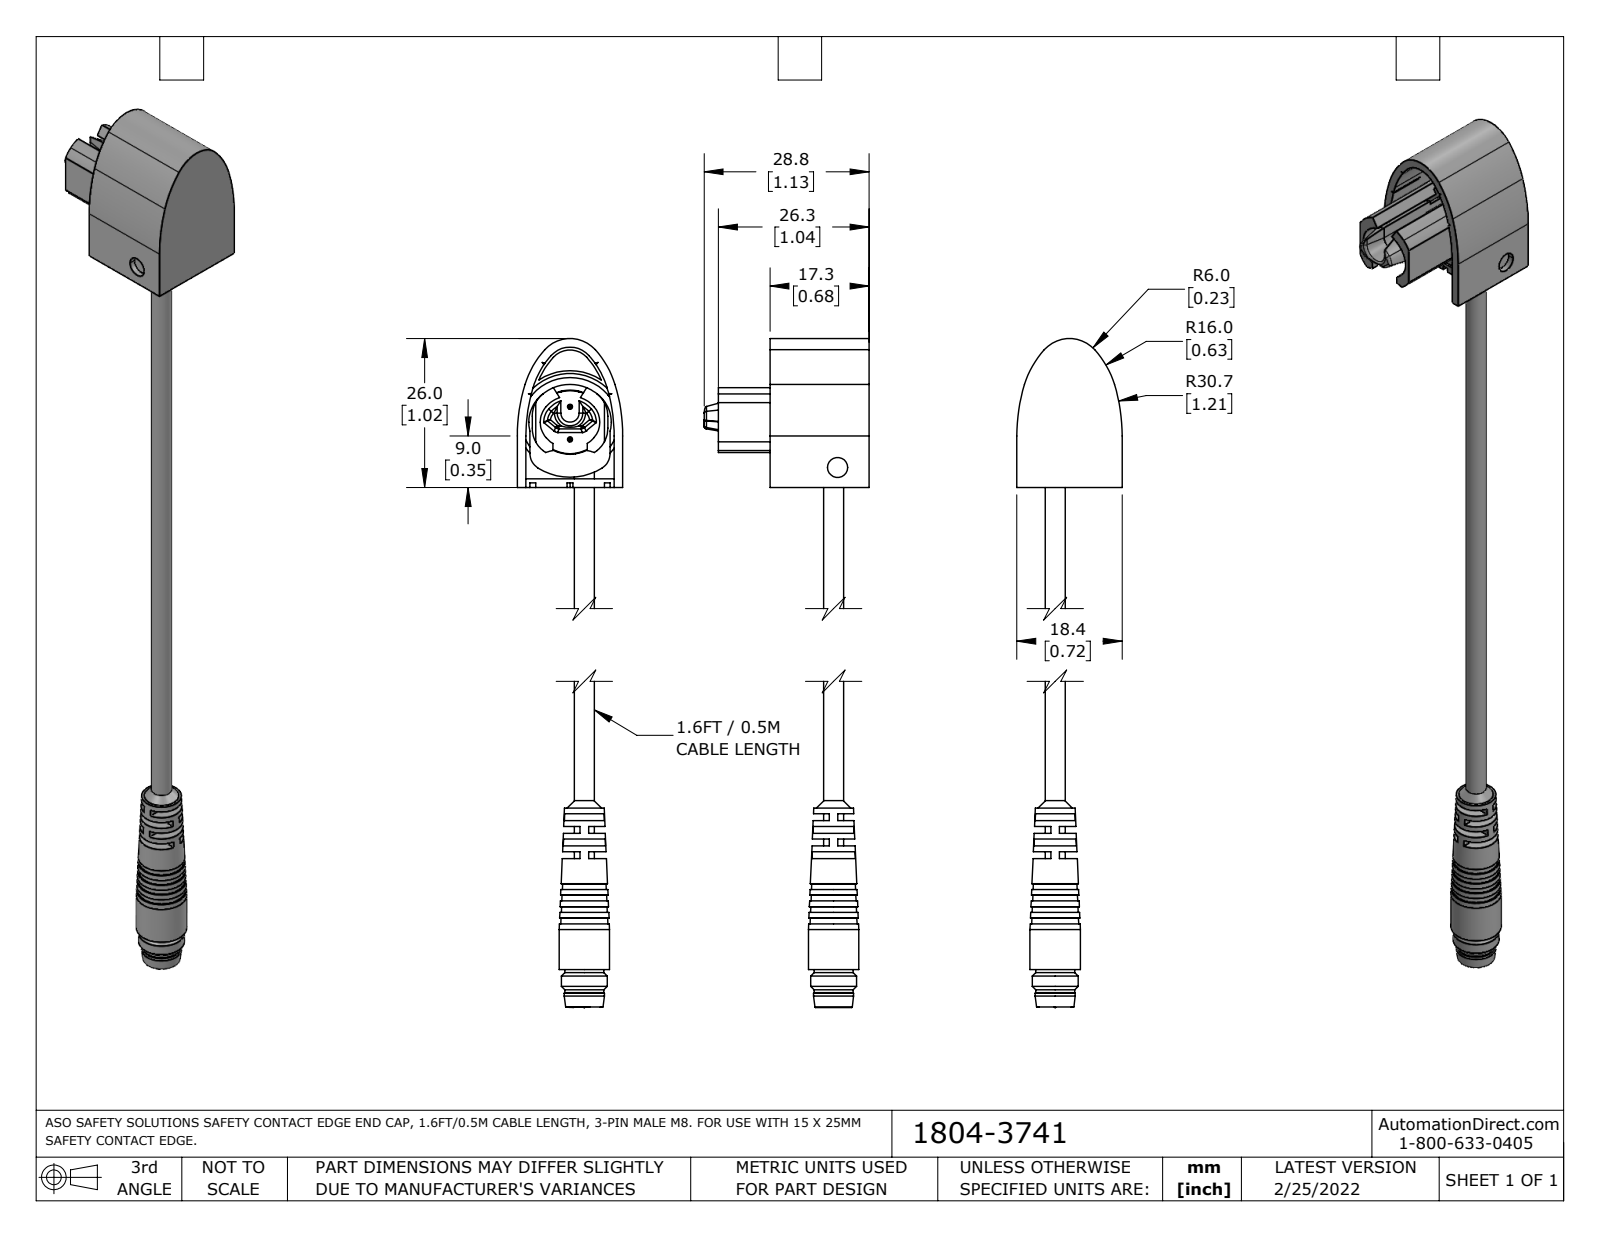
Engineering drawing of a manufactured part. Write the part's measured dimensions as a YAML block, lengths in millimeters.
part_name: "1804-3741_Default"
step_written_by: "SolidWorks 2021 (CONFIG_CONTROL_DESIGN)"
units: millimeters
bodies: {solids: 14, faces: 570, planar: 185, cylindrical: 235, other: 150}
overall_size: [173.9, 28.8, 18.4]
volume: 7808
surface_area: 10098
round_holes:
  - {diameter: 0.8, count: 3}
  - {diameter: 3.5, count: 2}
  - {diameter: 3.4, count: 1}
  - {diameter: 5.8, count: 1}
round_bosses_or_shafts:
  - {diameter: 1.2, count: 13}
  - {diameter: 0.5, count: 6}
  - {diameter: 1, count: 3}
  - {diameter: 1.66, count: 2}
  - {diameter: 0.9, count: 2}
  - {diameter: 0.6, count: 2}
  - {diameter: 8.8, count: 1}
  - {diameter: 8.4, count: 1}
partial_cylinders:
  - {radius: 0.1, count: 8}
  - {radius: 1, count: 8}
  - {radius: 0.5, count: 7}
  - {radius: 0.3, count: 6}
  - {radius: 5, count: 6}
  - {radius: 0.4, count: 2}
  - {radius: 2.9, count: 2}
  - {radius: 3, count: 2}
face_to_face_distances: [1.5, 3.2, 1, 16.9, 4.4, 8.8, 2.2, 7.6, 15.2, 1.7]
hole_center_spacings: [2, 2.6, 2.82, 5.7]
